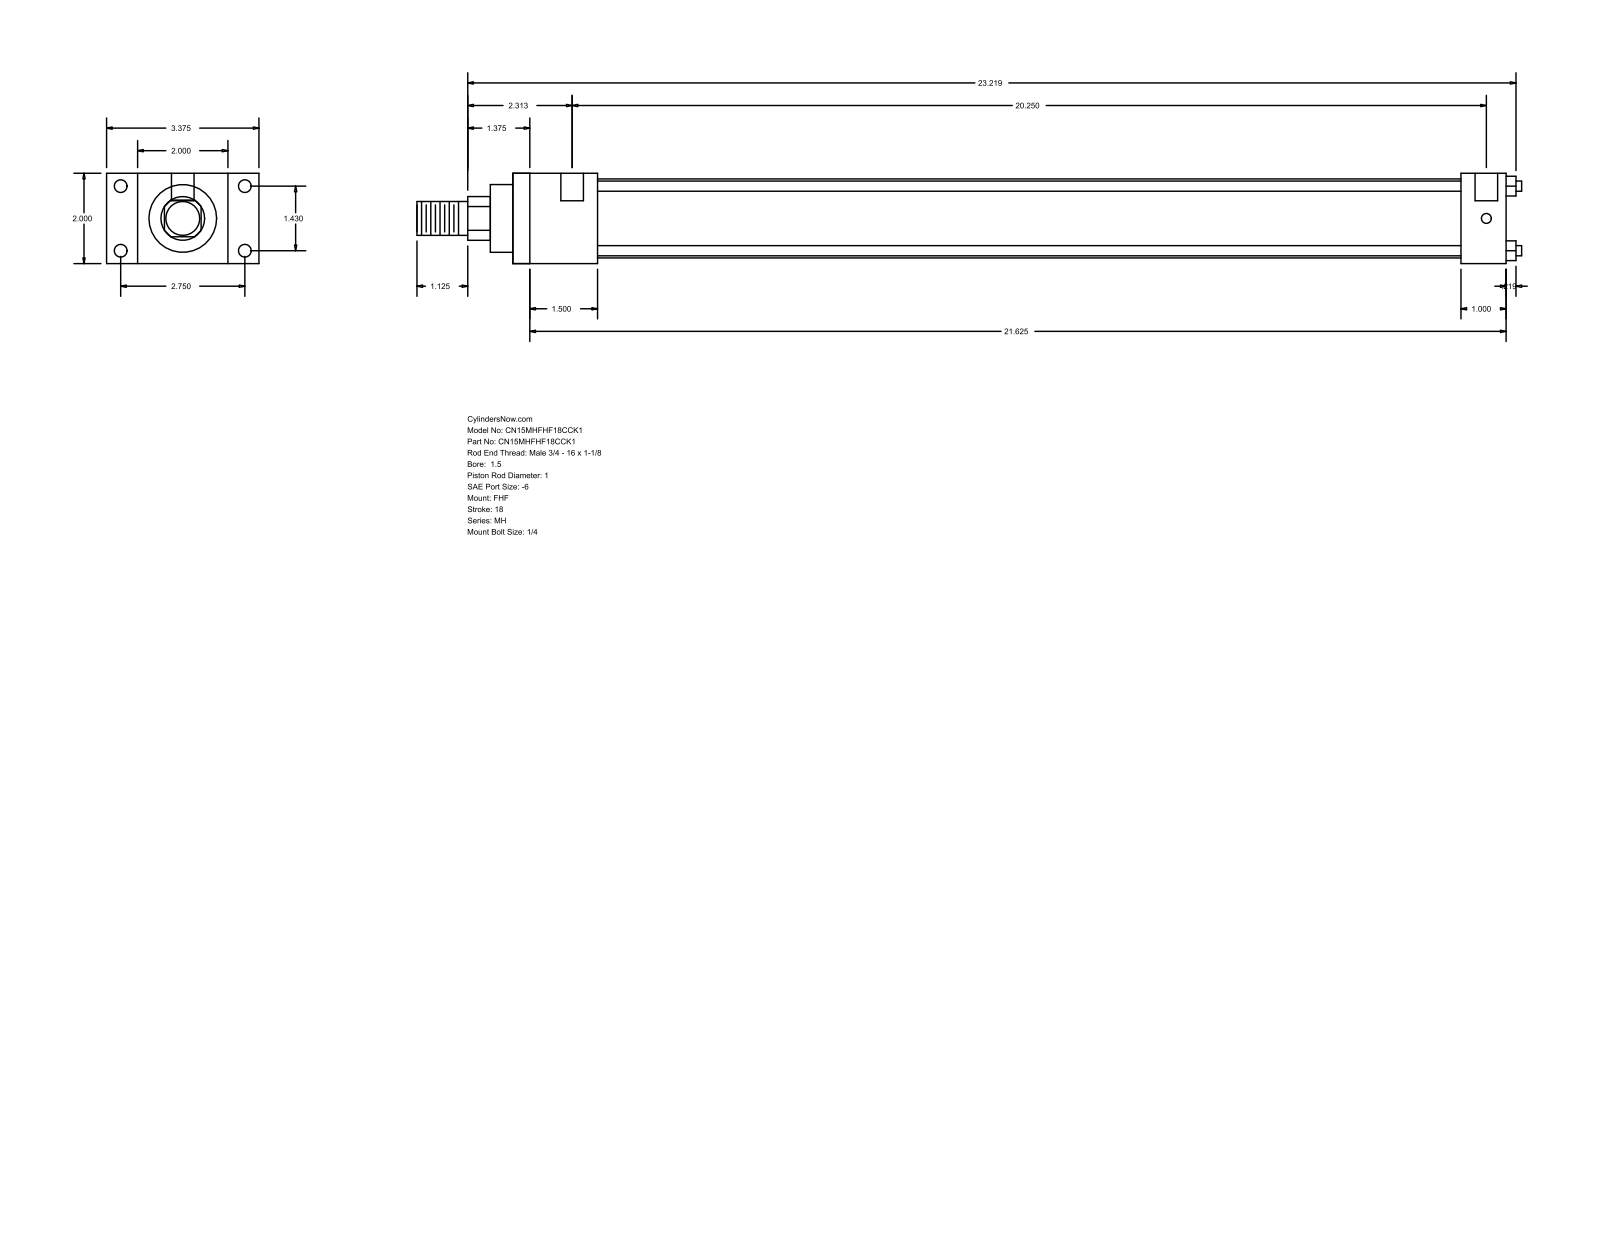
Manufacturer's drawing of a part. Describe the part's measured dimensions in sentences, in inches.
The part is named "MH_FHF__0150_1". Its 3-D file was written by "GSSL Pune (CONFIG_CONTROL_DESIGN)". It is 0 solids with 88 faces: 60 planar, 28 cylindrical and 0 other. Overall it measures 24.469 by 3.375 by 2 inches. Round holes: 4 of diameter 0.219, 4 of diameter 0.281, 2 of diameter 0.5. Round bosses or shafts: 4 of diameter 0.225, 1 of diameter 1.75, 1 of diameter 1.5, 1 of diameter 1, 1 of diameter 0.75. Partial cylindrical surfaces (rounded edges, fillets, slot ends): 1 of radius 0.484. The main face-to-face distances are 2, 0.687, 2.687, 1.875, 3.375, 22, 20.125, 1, 21, 19.125. The hole center spacings are 1.43, 2.75, 3.099, 20.375, 0.125, 20.25.
